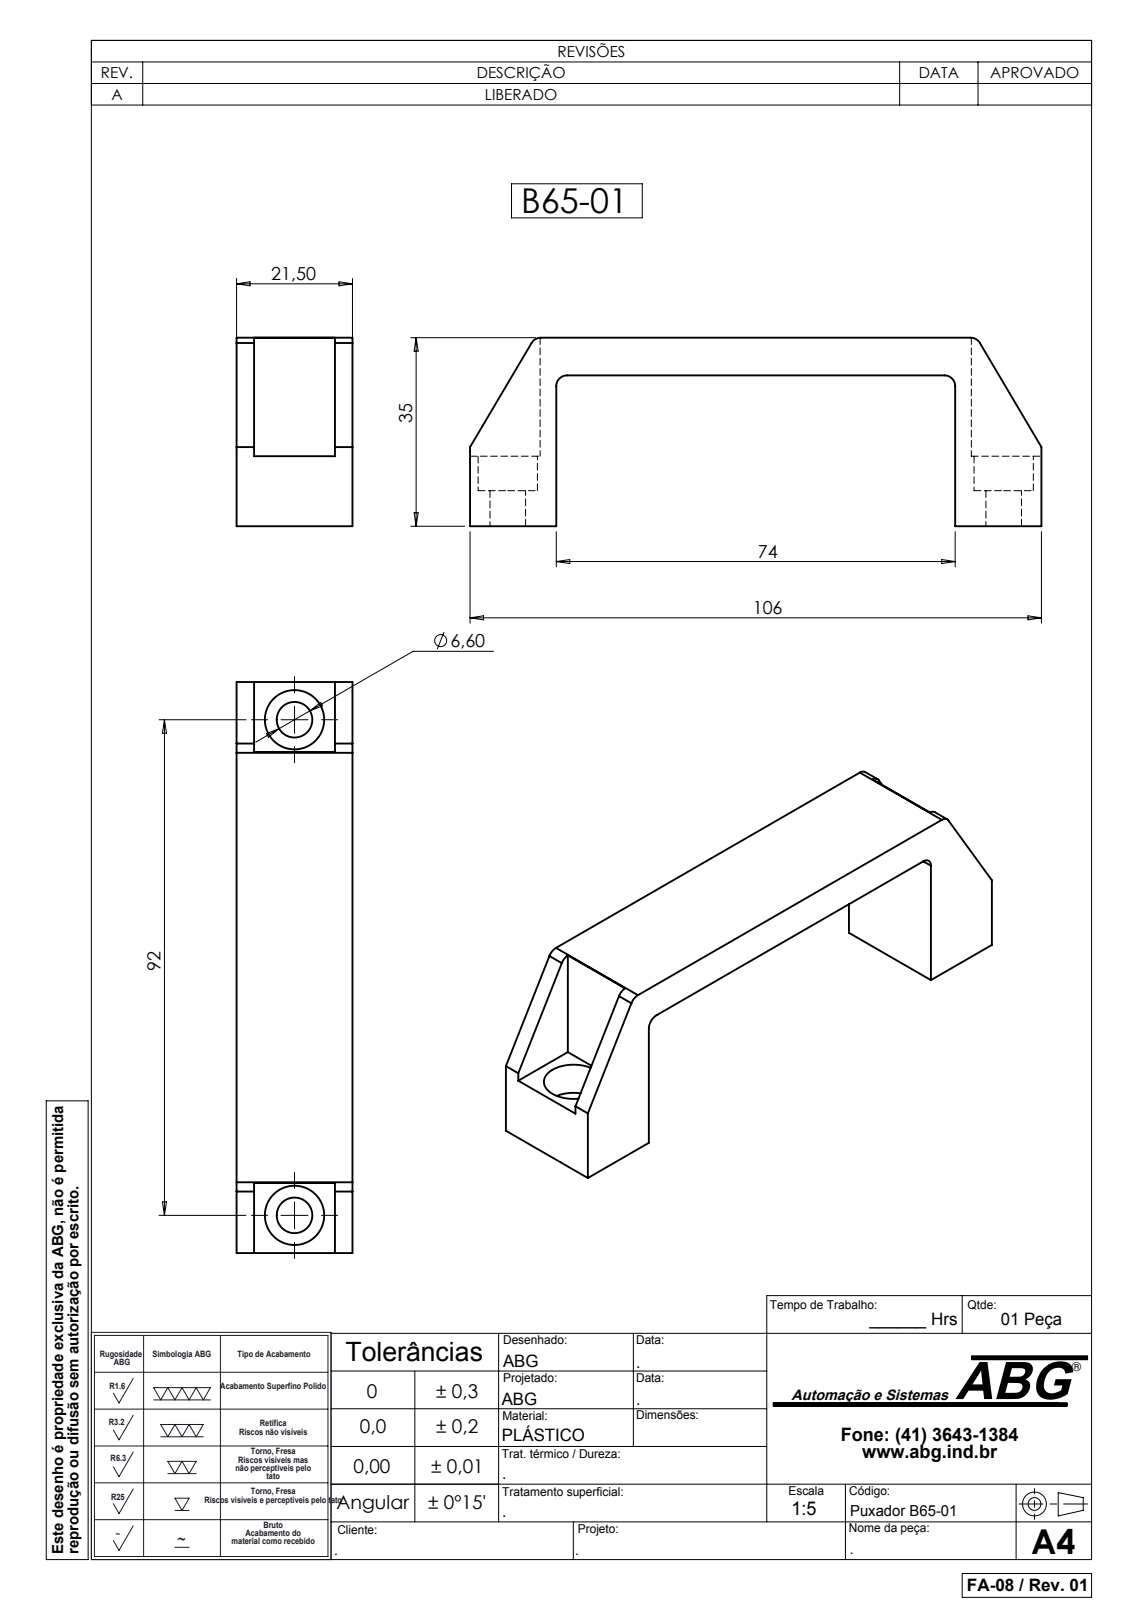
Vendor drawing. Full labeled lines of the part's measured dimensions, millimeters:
Part name (STEP PRODUCT): B65-01
STEP written by: SolidWorks 2007 (CONFIG_CONTROL_DESIGN)
Units: millimetres
Bodies: 1 solid, 36 faces (24 planar, 12 cylindrical, 0 other)
Overall size (bounding box): 106 × 35 × 21.5
Volume: 23 419 mm³ · Surface area: 11 140 mm²
Round holes (diameter × count): ⌀6.6 ×2, ⌀11 ×2
Partial cylindrical surfaces — rounded edges, fillets, slot ends (radius × count): R2 ×4
Main face-to-face distances: 7, 21.5, 13, 3, 77, 3.25, 18.25, 28, 35, 16
Hole centre spacings: 92
